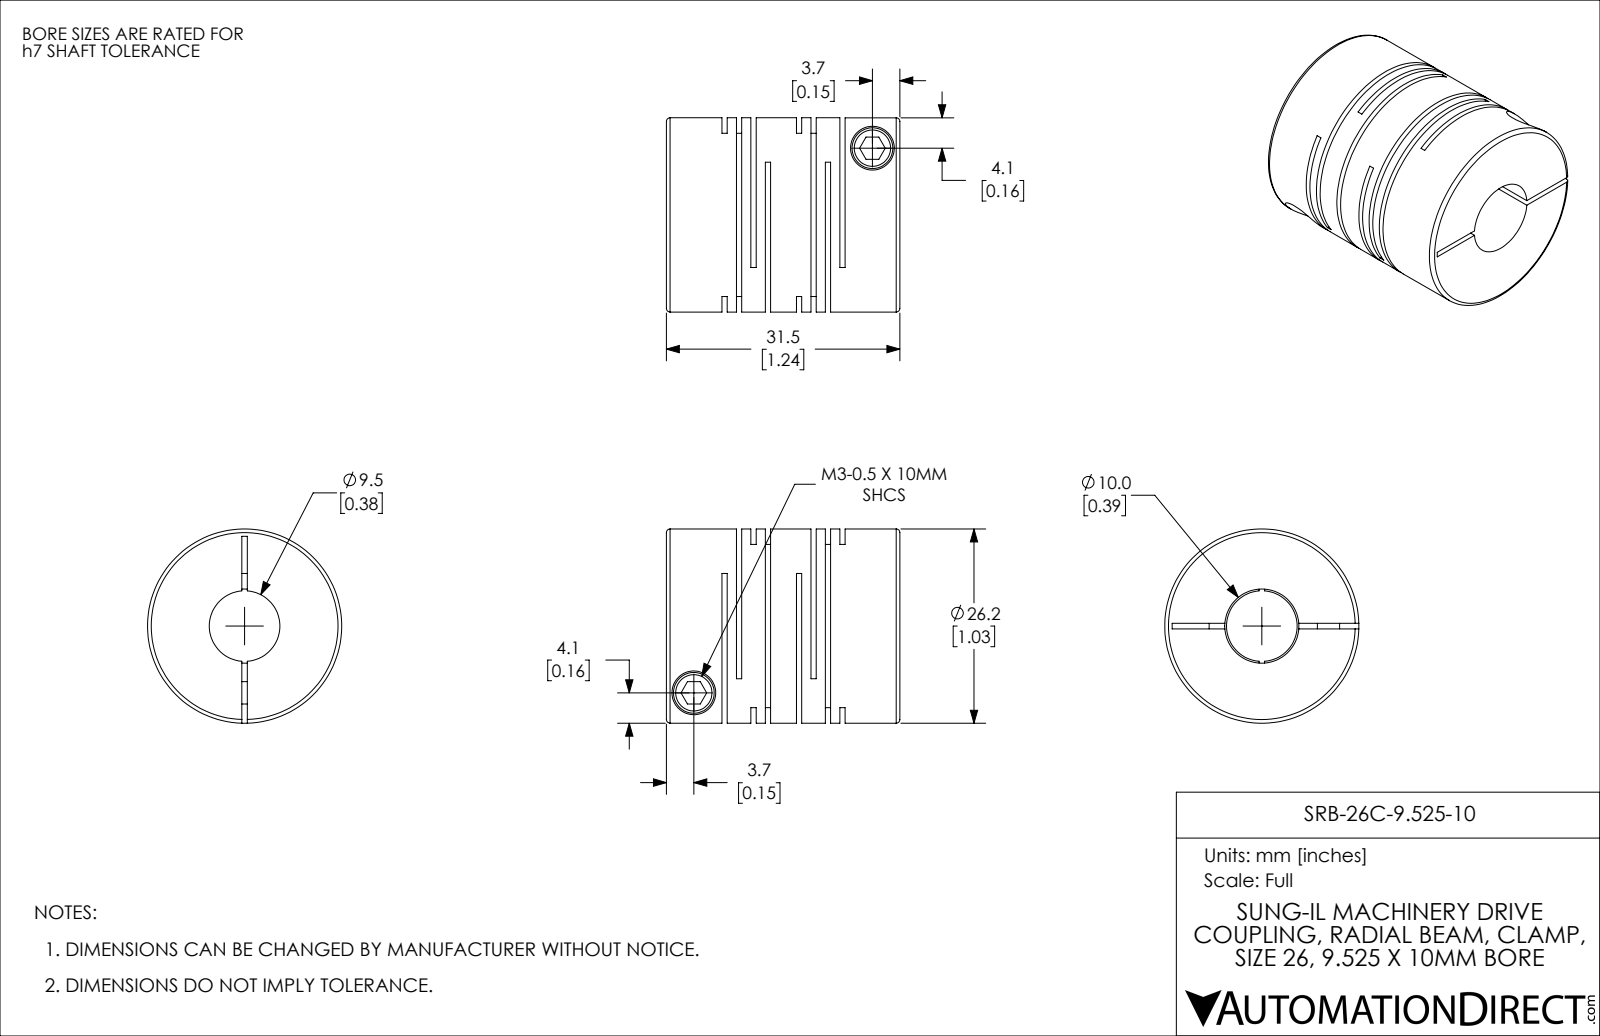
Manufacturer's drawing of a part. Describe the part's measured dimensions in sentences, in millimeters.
The part is named "SRB-26C-9.525-10". Its 3-D file was written by "SolidWorks 2021 (CONFIG_CONTROL_DESIGN)". It is 1 solid with 114 faces: 60 planar, 42 cylindrical and 12 other. Overall it measures 31.5 by 26.2 by 26.2 millimeters. Its volume is 11 995 cubic millimeters and its surface area 10 735 square millimeters. Round holes: 2 of diameter 3, 2 of diameter 5.9, 1 of diameter 9.53, 1 of diameter 10. Round bosses or shafts: 2 of diameter 5.5, 1 of diameter 26.2. The main face-to-face distances are 1.95, 10.05, 0.71, 3.9, 8.1, 12, 1.24, 2.66, 9.34, 13.95.
